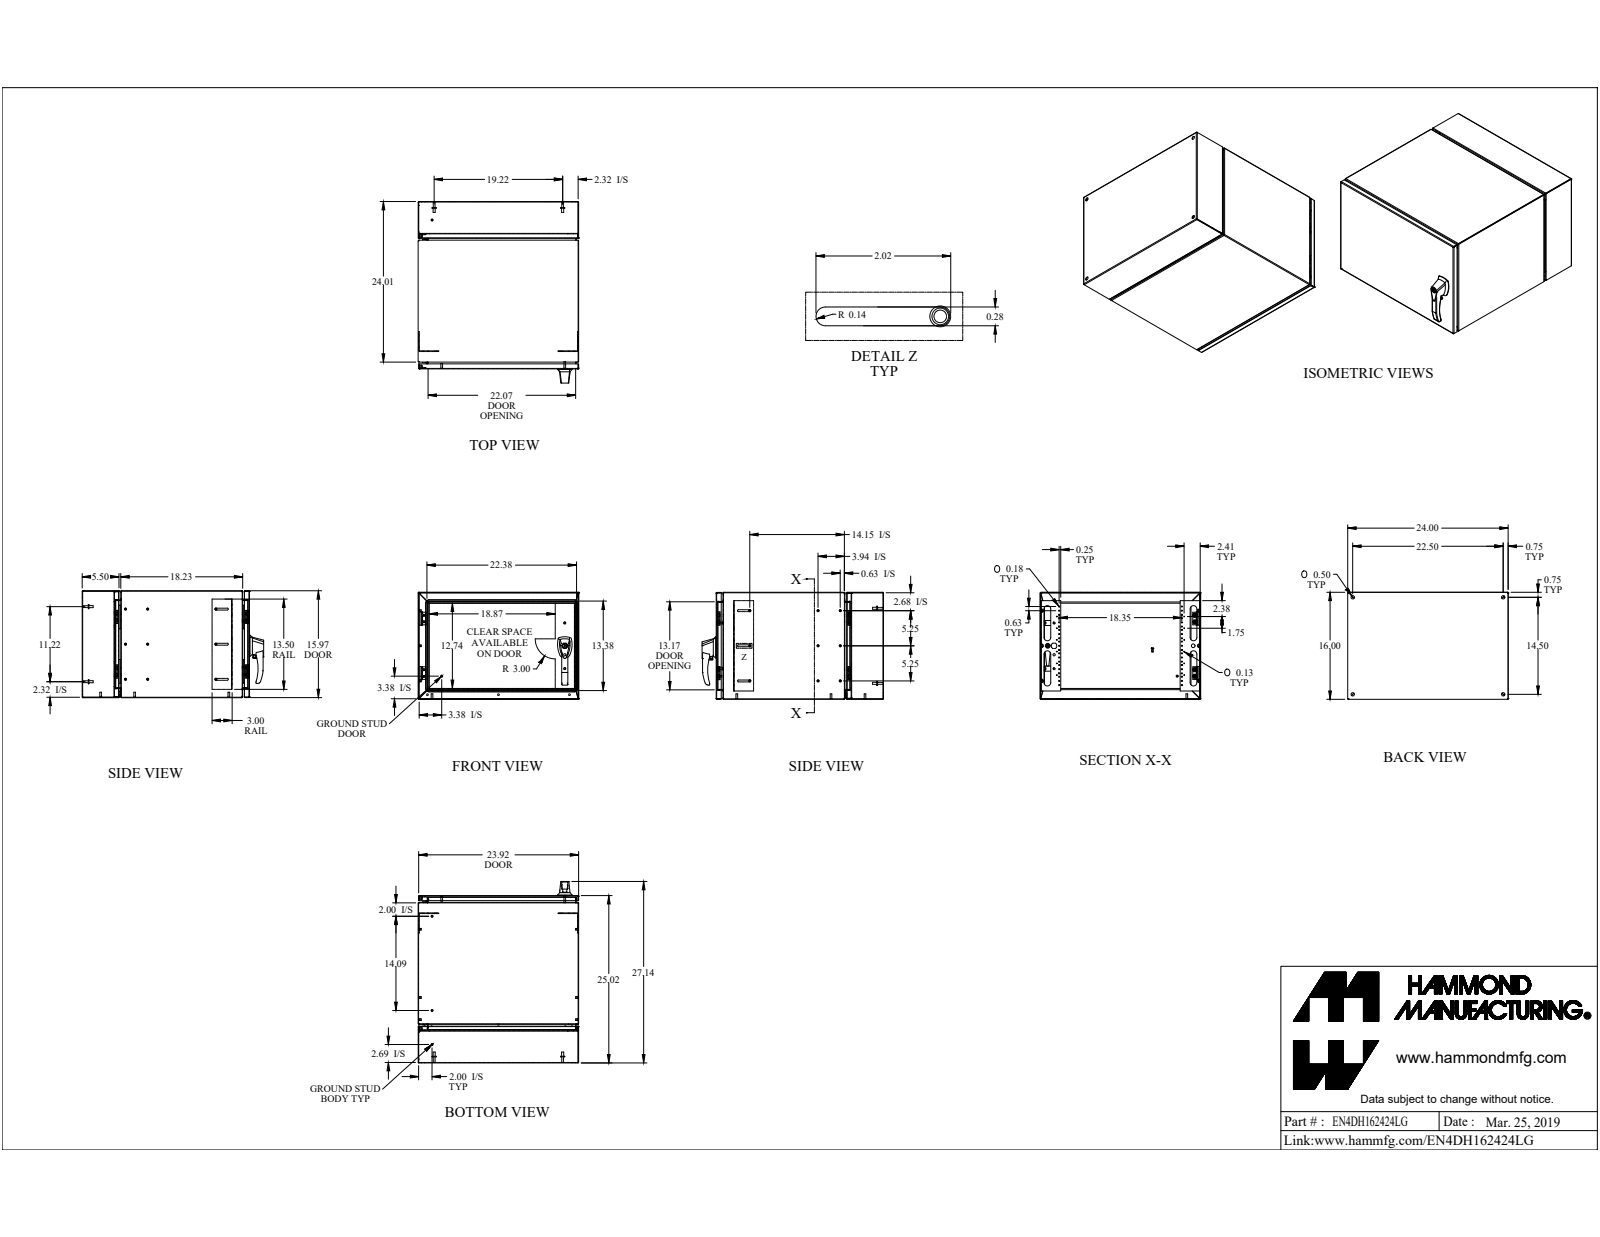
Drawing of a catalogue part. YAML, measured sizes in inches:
part_name: "EN4DH162424LG"
step_written_by: "SolidWorks 2019 (CONFIG_CONTROL_DESIGN)"
units: inches
bodies: {solids: 179, faces: 3622, planar: 1992, cylindrical: 919, other: 711}
overall_size: [27.135, 24.001, 16]
volume: 293.5
surface_area: 7592
round_holes:
  - {diameter: 0.177, count: 42}
  - {diameter: 0.25, count: 17}
  - {diameter: 0.196, count: 15}
  - {diameter: 0.125, count: 12}
  - {diameter: 0.188, count: 8}
  - {diameter: 0.194, count: 8}
  - {diameter: 0.237, count: 8}
  - {diameter: 0.257, count: 7}
  - {diameter: 0.275, count: 7}
  - {diameter: 0.265, count: 5}
  - {diameter: 0.276, count: 4}
  - {diameter: 0.281, count: 4}
round_bosses_or_shafts:
  - {diameter: 0.25, count: 24}
  - {diameter: 0.313, count: 16}
  - {diameter: 0.236, count: 10}
  - {diameter: 0.625, count: 9}
  - {diameter: 0.472, count: 8}
  - {diameter: 0.433, count: 8}
  - {diameter: 0.187, count: 8}
  - {diameter: 0.281, count: 6}
partial_cylinders:
  - {radius: 0.036, count: 38}
  - {radius: 0.108, count: 38}
  - {radius: 0.02, count: 34}
  - {radius: 0.141, count: 18}
  - {radius: 0.25, count: 18}
  - {radius: 0.125, count: 17}
  - {radius: 0.06, count: 16}
  - {radius: 0.079, count: 12}
face_to_face_distances: [0.072, 24.948, 0.072, 23.928, 15.928, 15.928, 16, 15.856, 23.856, 24.876]
hole_center_spacings: [1.933, 3.5, 5.25, 14.506, 22.272, 0.985, 1.125, 1.125]
